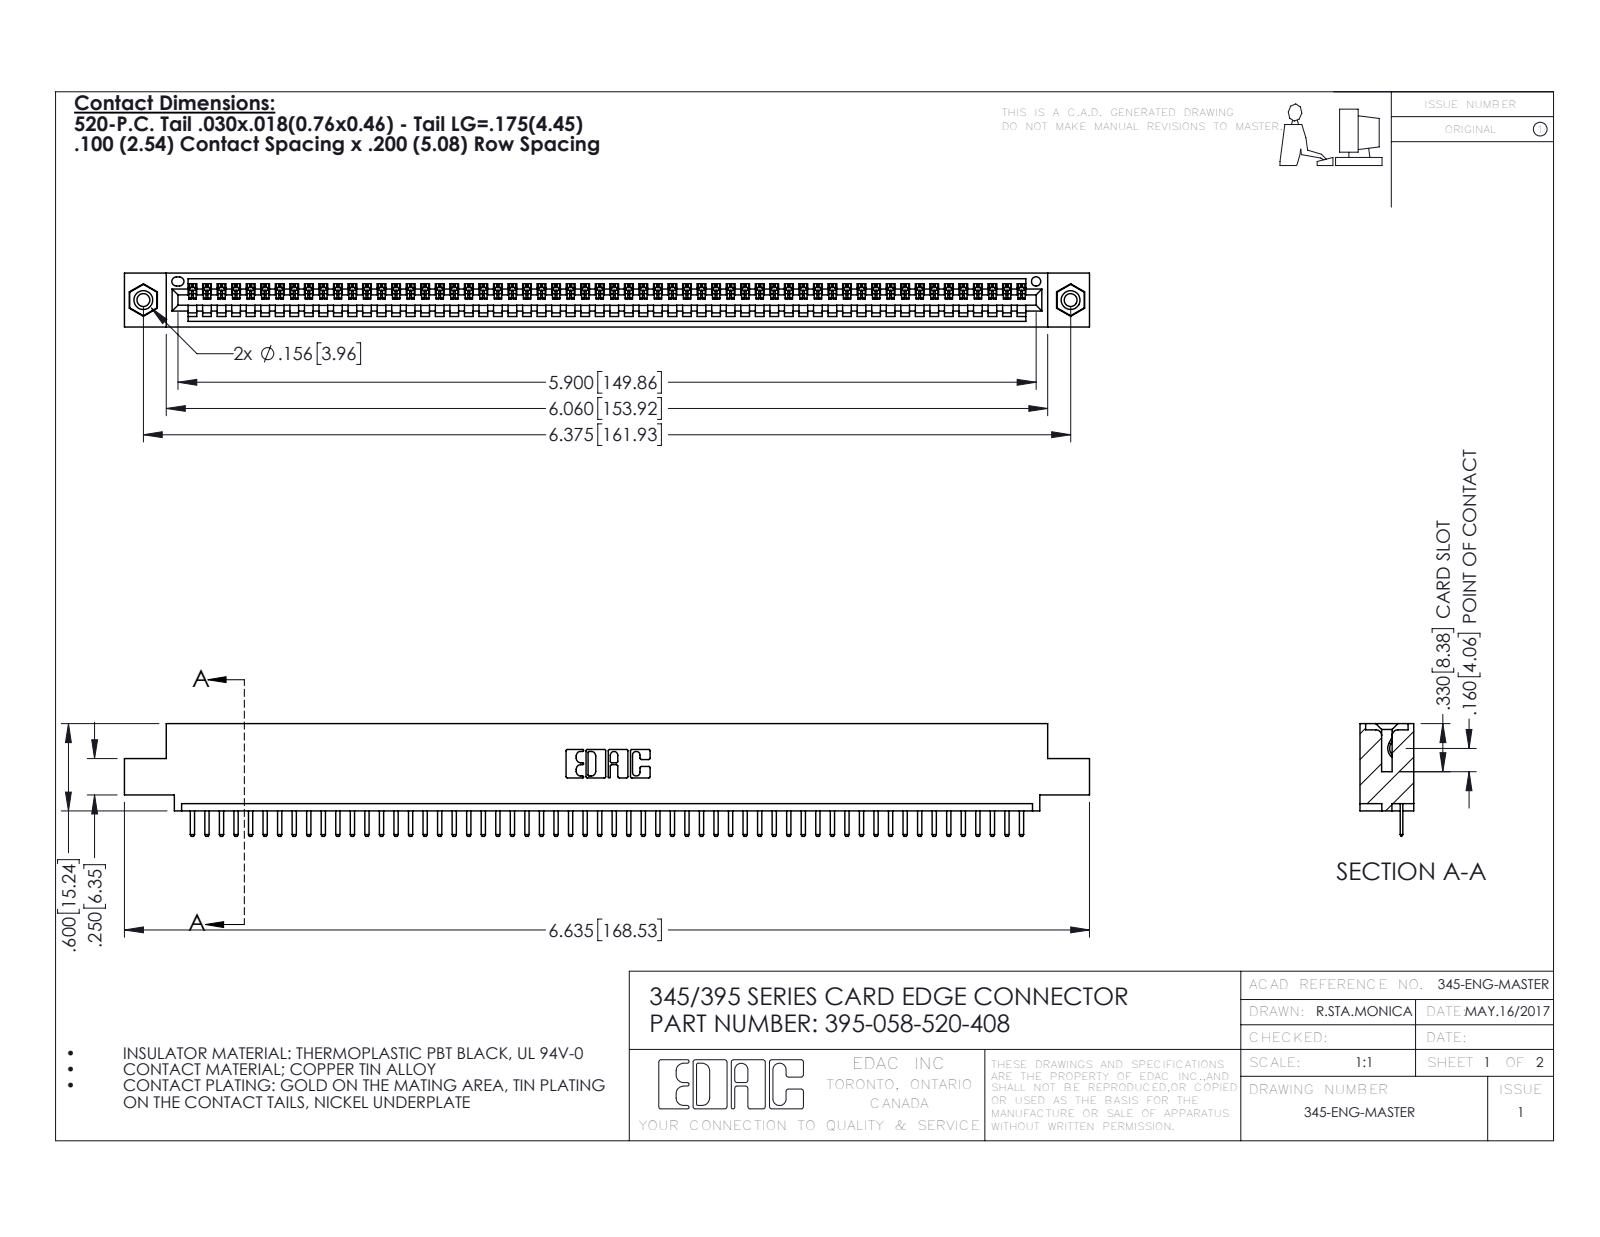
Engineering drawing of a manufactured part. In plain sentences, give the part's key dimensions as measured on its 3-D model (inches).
The part is named "345-292-001_345-293-120; 395-058-520-408; 345 Part_0.110 Offset - 0.156 Dia-TI; 345-250-001_345-250-003-102". Its 3-D file was written by "SolidWorks 2016 (CONFIG_CONTROL_DESIGN)". It is 61 solids with 3786 faces: 2552 planar, 1218 cylindrical and 16 other. Overall it measures 6.635 by 0.775 by 0.37 inches. Its volume is 0.97 cubic inches and its surface area 32.38 square inches. Round holes: 2 of diameter 0.089, 2 of diameter 0.125, 2 of diameter 0.156, 1 of diameter 0.064. Round bosses or shafts: 2 of diameter 0.155. Partial cylindrical surfaces (rounded edges, fillets, slot ends): 118 of radius 0.01, 116 of radius 0.006, 22 of radius 0.01, 6 of radius 0.007, 6 of radius 0.031, 3 of radius 0.026, 2 of radius 0.031, 2 of radius 0.04. The main face-to-face distances are 0.072, 0.298, 0.37, 0.2, 0.098, 0.272, 0.025, 0.225, 0.072, 0.149. The hole center spacings are 0.27, 6.139, 6.375.
